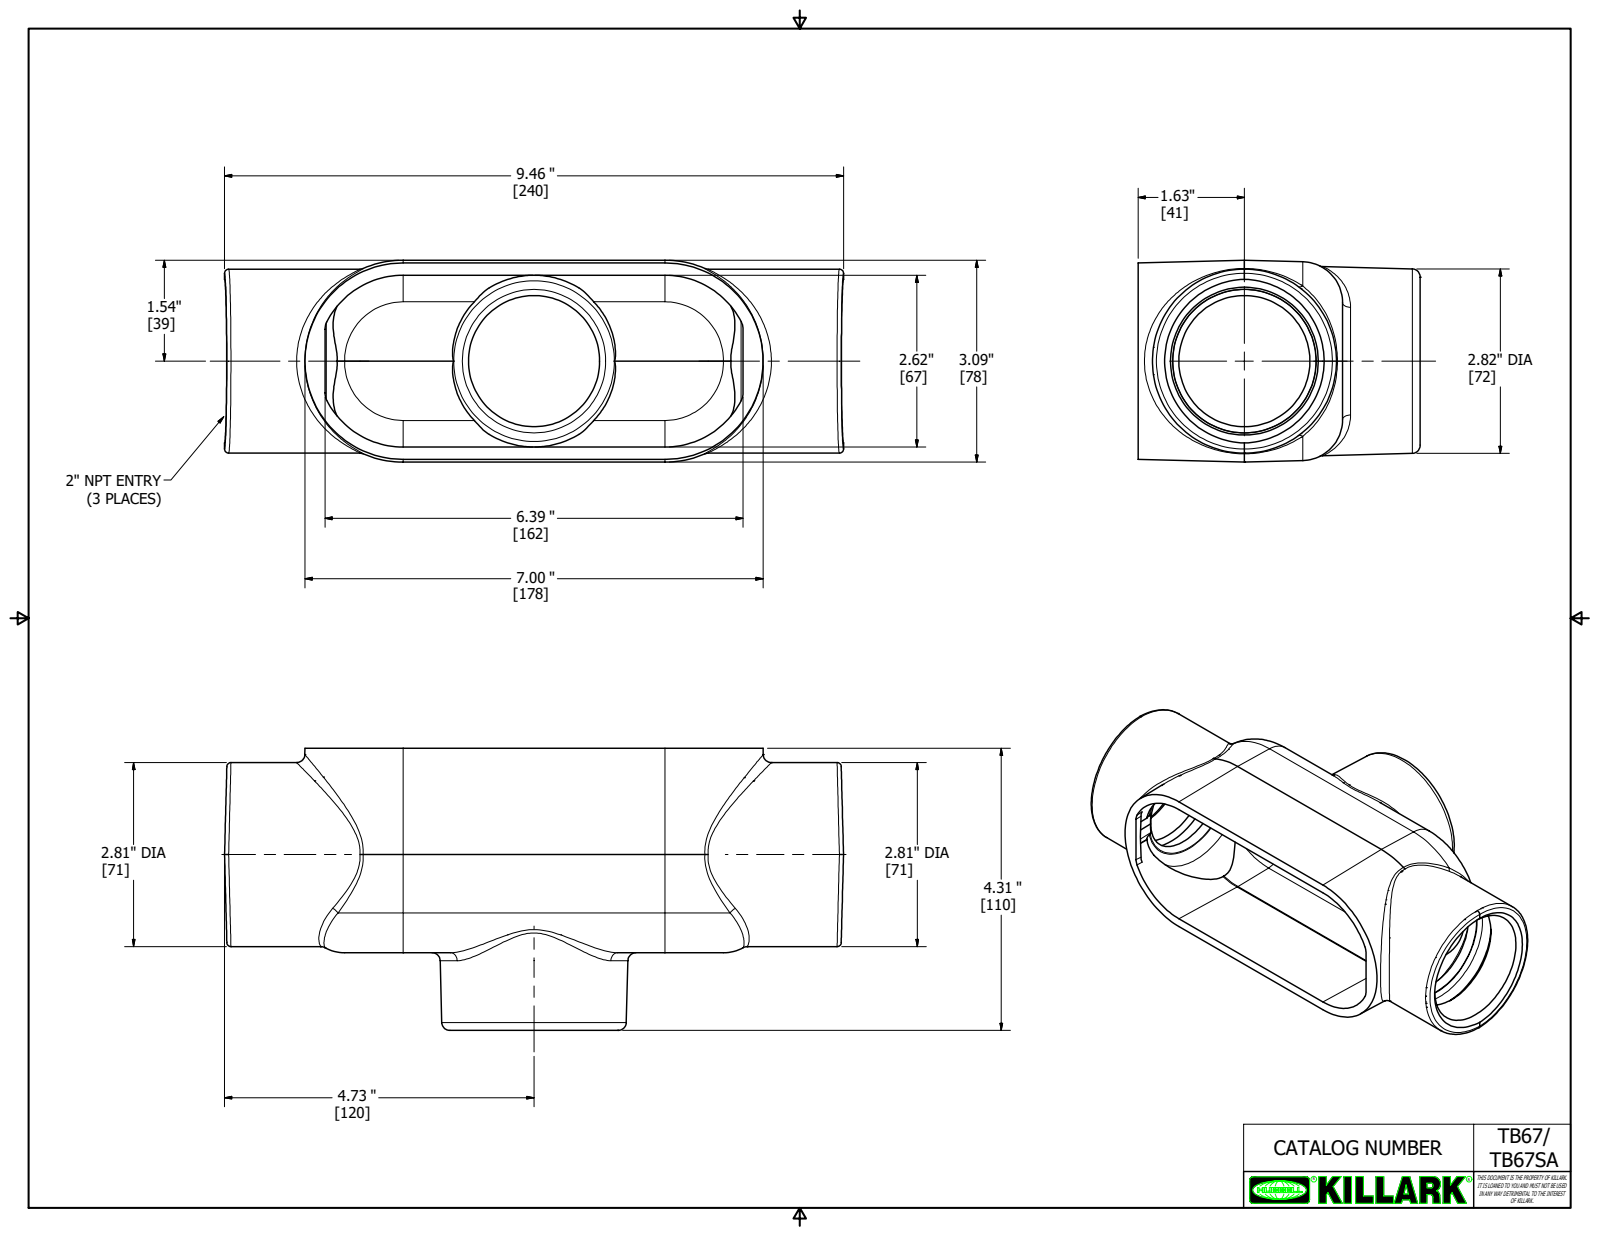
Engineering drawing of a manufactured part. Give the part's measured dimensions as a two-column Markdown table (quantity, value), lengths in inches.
| quantity | value |
| --- | --- |
| part name | 17714 |
| STEP written by | Autodesk Inventor 2018 (AUTOMOTIVE_DESIGN) |
| units | inches |
| bodies | 1 solid, 142 faces (50 planar, 27 cylindrical, 65 other) |
| overall size | 9.46 × 4.313 × 3.085 |
| volume | 18.76 in³ |
| surface area | 183.1 in² |
| round holes (diameter × count) | 2.381 × 2, 2.594 × 1 |
| round bosses / shafts (diameter × count) | 2.812 × 1 |
| partial cylindrical surfaces (radius × count) | 0.06 × 8, 0.05 × 4, 0.437 × 2, 0.5 × 2, 0.625 × 2, 1.312 × 1 |
| main face-to-face distances | 0.187, 2.898, 3.085, 2.71, 3.125, 2.937, 9.46, 0.031, 0.156, 3.094 |
